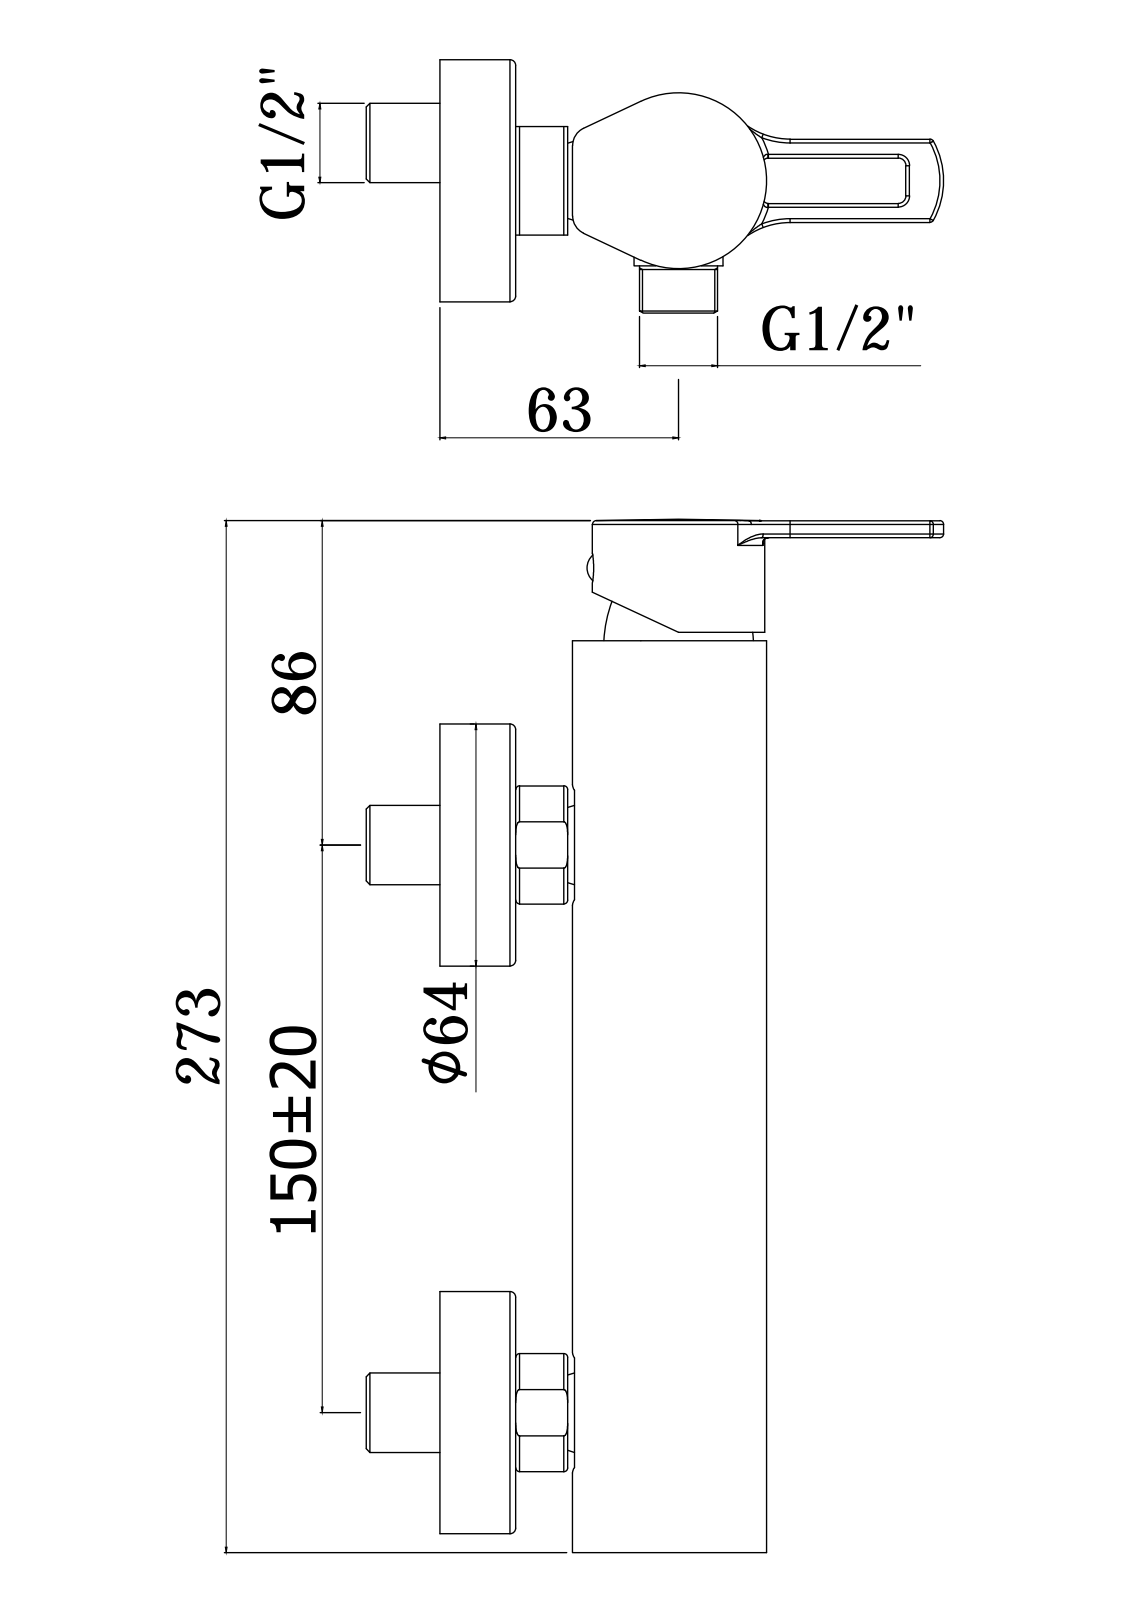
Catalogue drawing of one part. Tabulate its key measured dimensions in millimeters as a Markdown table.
| quantity | value |
| --- | --- |
| part name | RIN168CR |
| STEP written by | CREO PARAMETRIC BY PTC INC, 2020044 (CONFIG_CONTROL_DESIGN) |
| units | millimeters |
| bodies | 2 solids, 1558 faces (741 planar, 428 cylindrical, 389 other) |
| overall size | 273 × 132.95 × 66.7 |
| volume | 267 842 mm³ |
| surface area | 164 629 mm² |
| round holes (diameter × count) | 7 × 3, 20 × 3, 4 × 2, 9.5 × 2, 10.5 × 2, 18 × 2, 21.6 × 2, 62.3 × 2, 2.5 × 1, 3 × 1, 3.3 × 1, 3.5 × 1 |
| round bosses / shafts (diameter × count) | 63.5 × 2, 27 × 2, 26.2 × 2, 23 × 2, 20.5 × 2, 17.7 × 2, 45.5 × 1, 35.5 × 1 |
| partial cylindrical surfaces (radius × count) | 1.5 × 44, 0.5 × 34, 1 × 14, 0.15 × 11, 0.3 × 4, 1.3 × 4, 6 × 4, 2 × 2 |
| main face-to-face distances | 3.7, 0.6, 3.5, 29.8, 29.2, 15, 10.5, 26.3, 14.2, 25.7 |
| hole center spacings | 7.07, 8.6, 11.4, 150, 4, 6, 10, 11 |
